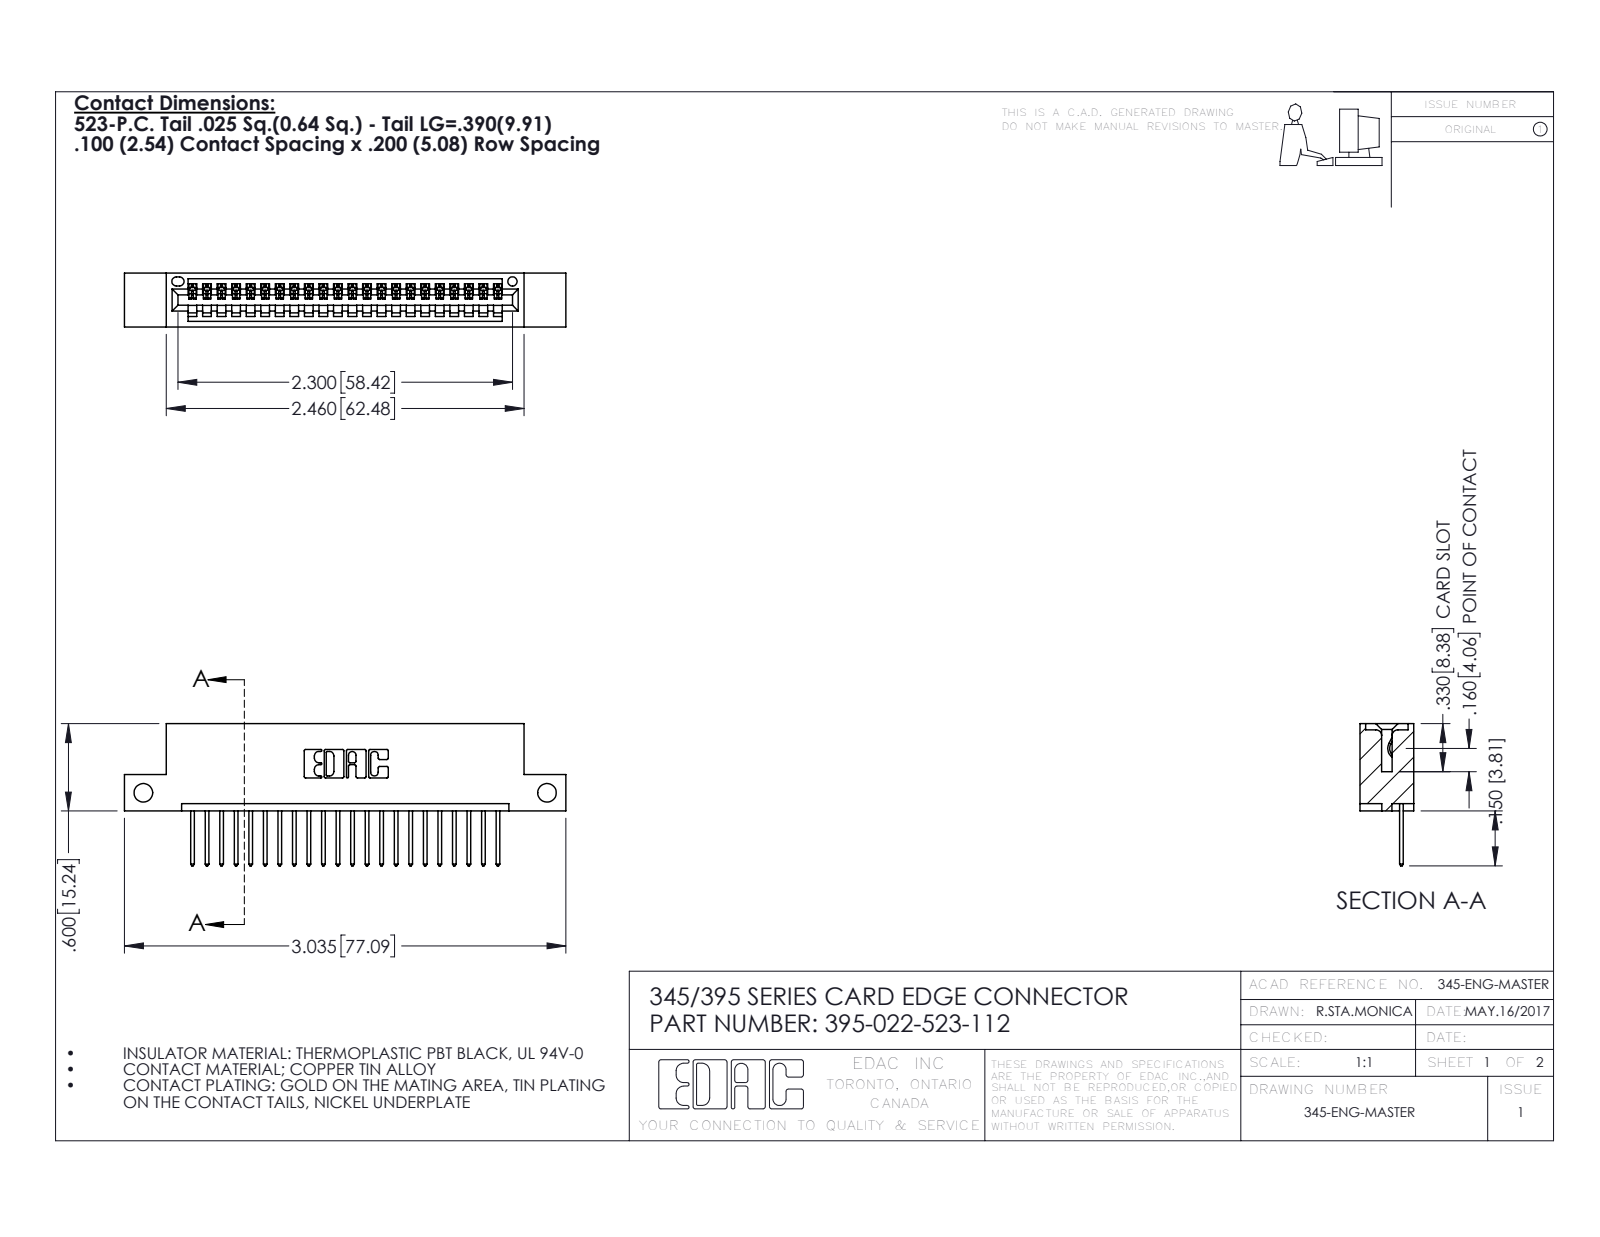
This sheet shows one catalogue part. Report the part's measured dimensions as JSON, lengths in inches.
{"part_name": "345-292-001_345-293-123; 395-022-523-112; 345 Part_Flush Mounting Lugs - Side Mount", "step_written_by": "SolidWorks 2016 (CONFIG_CONTROL_DESIGN)", "units": "inches", "bodies": {"solids": 23, "faces": 1402, "planar": 960, "cylindrical": 442, "other": 0}, "overall_size": [3.035, 0.977, 0.37], "volume_in3": 0.431, "surface_area_in2": 13.94, "round_holes": [[0.128, 2], [0.064, 1]], "partial_cylinders_radius": [[0.006, 44], [0.01, 44], [0.01, 22], [0.007, 6], [0.031, 6], [0.026, 3], [0.031, 2], [0.04, 2]], "face_to_face_distances": [0.298, 0.072, 0.2, 0.37, 0.098, 0.272, 0.025, 0.225, 0.149, 0.05], "hole_center_spacings": [2.775]}
